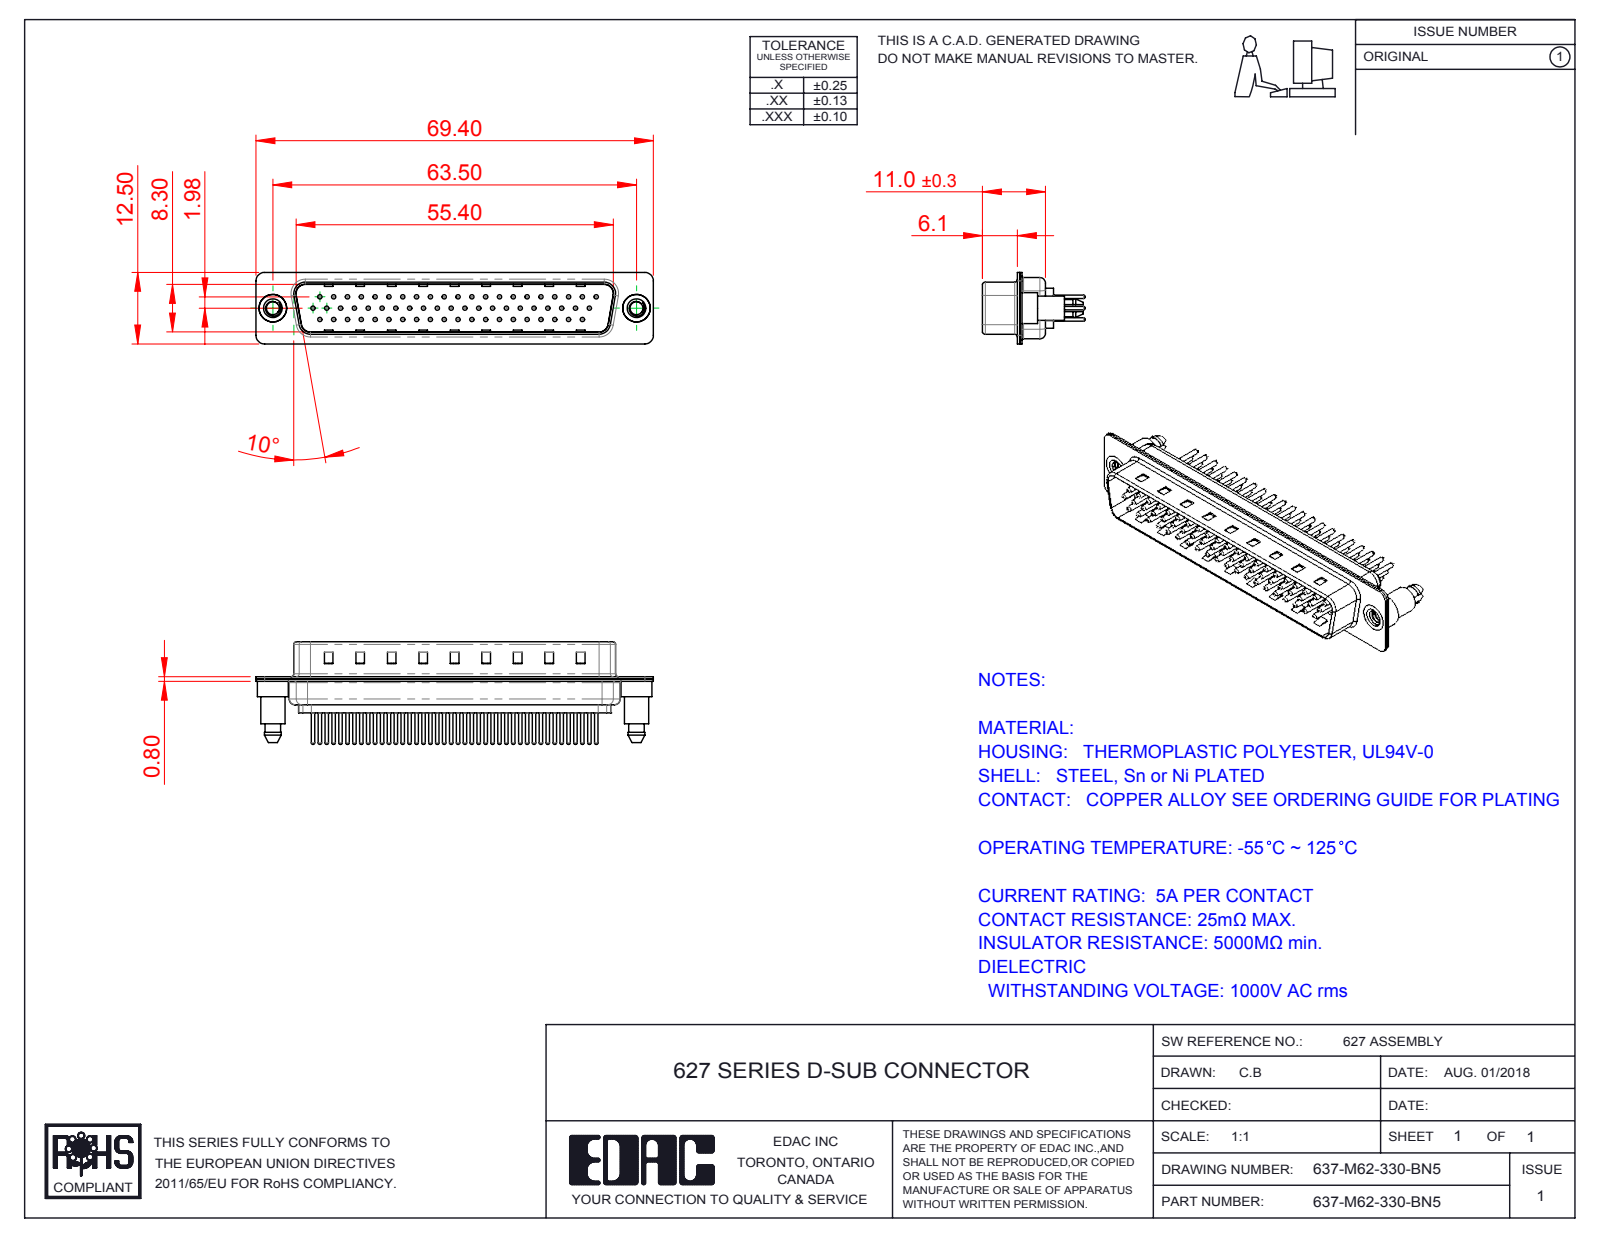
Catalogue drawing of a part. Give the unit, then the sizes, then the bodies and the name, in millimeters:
Units: millimetres
Overall size (bounding box): 69.4 × 17.9 × 12.5
Round holes (diameter × count): ⌀0.75 ×62, ⌀1.6 ×62, ⌀2 ×62, ⌀2.26 ×2, ⌀4 ×2, ⌀4.8 ×2
Round bosses / shafts (diameter × count): ⌀1.5 ×62, ⌀0.6 ×62, ⌀5.4 ×2, ⌀4.9 ×2, ⌀4.25 ×2
Partial cylindrical surfaces — rounded edges, fillets, slot ends (radius × count): R1.5 ×18, R2 ×12, R1.6 ×10, R0.5 ×8, R0.25 ×4, R0.6 ×4, R0.65 ×4, R0.9 ×4
Main face-to-face distances: 0.4, 0.8, 9.5, 9.1, 8.7, 9.9, 0.75, 0.35, 5.9, 1.2
Hole centre spacings: 7.24, 2.32, 2.41, 4.13, 9.65, 4.83, 14.48, 11.04
Volume: 4 051 mm³ · Surface area: 11 746 mm²
Bodies: 67 solids, 2756 faces (653 planar, 1041 cylindrical, 1062 other)
Part name (STEP PRODUCT): 637M Shell Rear_62 Contacts; 637-M62-330-BN5; 637M 4-40 Threaded Boardlock; 637M Shell Front_62 Contacts (+4 more)
STEP written by: SolidWorks 2016 (CONFIG_CONTROL_DESIGN)
